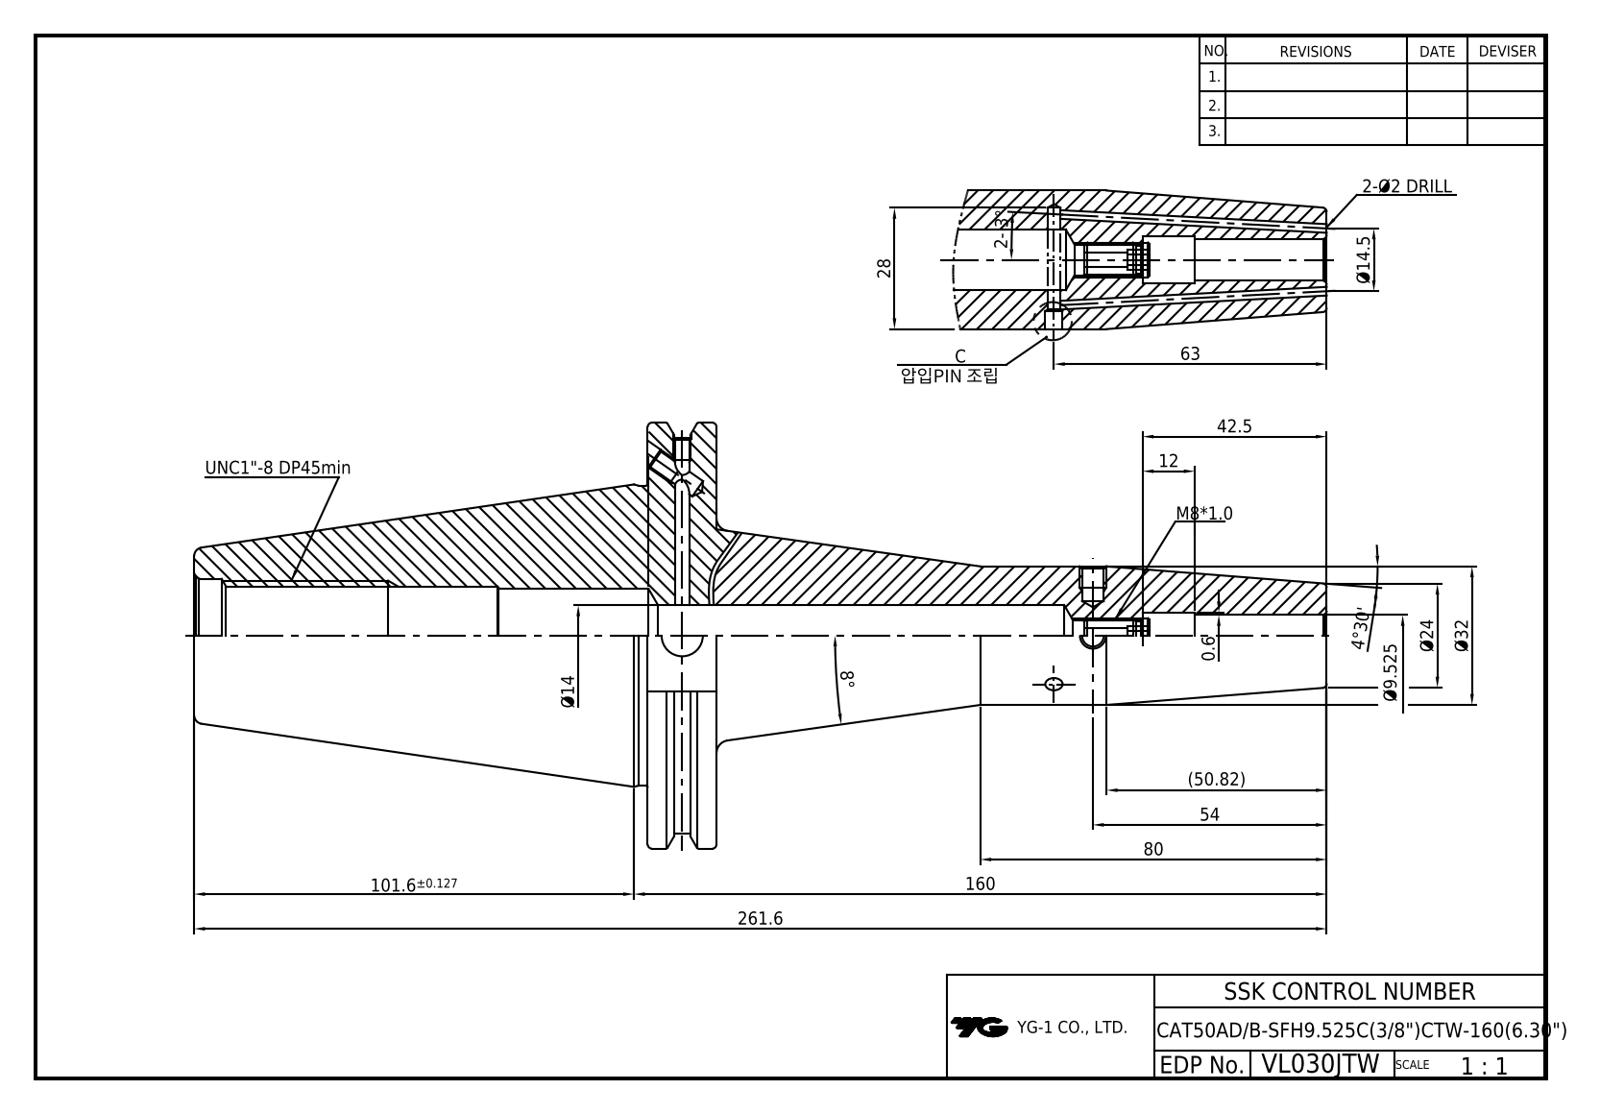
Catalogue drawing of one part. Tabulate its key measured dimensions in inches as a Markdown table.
| quantity | value |
| --- | --- |
| part name | CAT50_SHANK_20130708 |
| STEP written by | CREO PARAMETRIC BY PTC INC, 2018500 (CONFIG_CONTROL_DESIGN) |
| units | inches |
| bodies | 1 solid, 102 faces (30 planar, 30 cylindrical, 42 other) |
| overall size | 10.305 × 3.875 × 3.718 |
| volume | 27.07 in³ |
| surface area | 101.8 in² |
| round holes (diameter × count) | 0.375 × 2, 0.315 × 1, 0.422 × 1, 0.551 × 1, 0.807 × 1, 0.827 × 1, 0.945 × 1, 0.984 × 1, 1.008 × 1 |
| round bosses / shafts (diameter × count) | 3.875 × 1, 3.594 × 1, 2.726 × 1, 1.26 × 1 |
| main face-to-face distances | 0.626, 4.13, 4.756, 2.875, 10.305, 6.175, 5.549, 1.012, 4.37, 0.24 |
